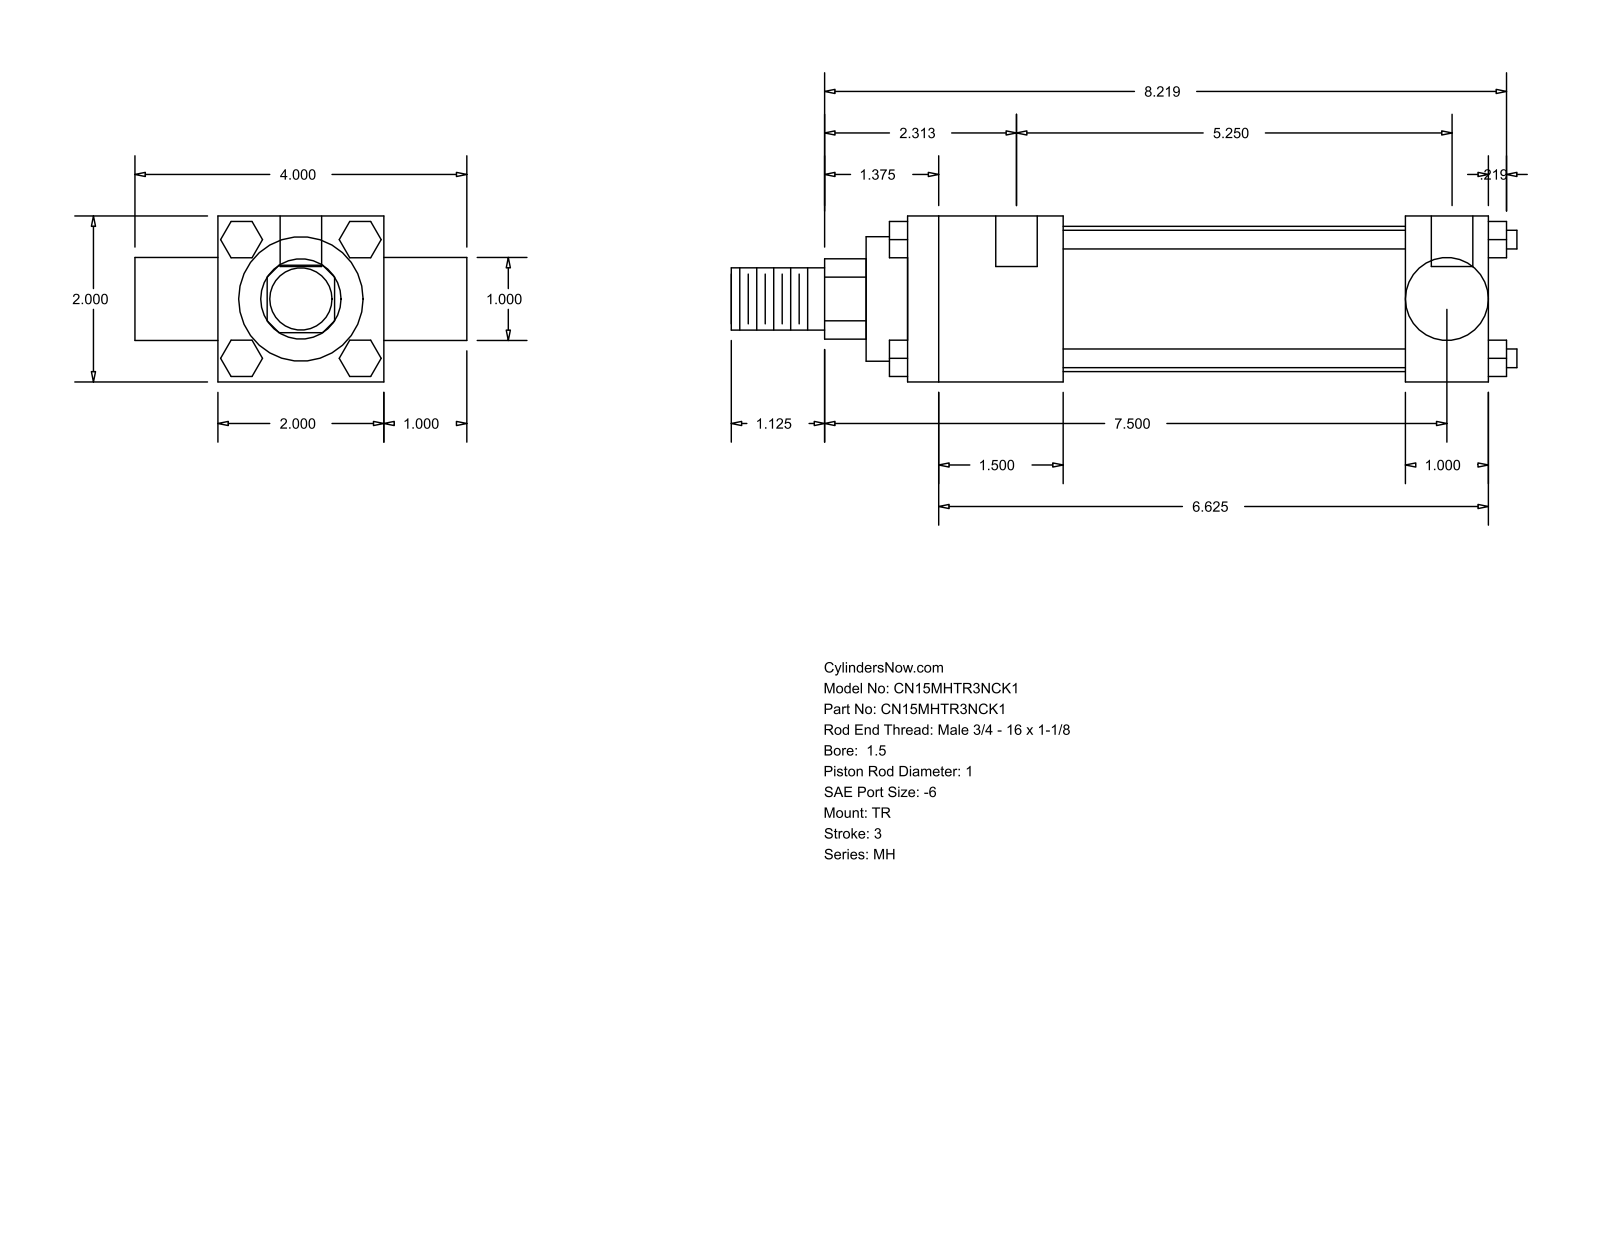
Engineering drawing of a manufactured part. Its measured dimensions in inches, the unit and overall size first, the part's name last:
Units: inches
Overall size (bounding box): 9.469 × 4 × 2
Round holes (diameter × count): ⌀0.219 ×3, ⌀0.5 ×2
Round bosses / shafts (diameter × count): ⌀0.225 ×4, ⌀1.75 ×1, ⌀1.5 ×1, ⌀1 ×1, ⌀0.998 ×1, ⌀0.75 ×1
Partial cylindrical surfaces — rounded edges, fillets, slot ends (radius × count): R0.484 ×1
Main face-to-face distances: 2, 1, 7, 3, 1.875, 5.125, 6, 4.125, 4, 0.5
Hole centre spacings: 0.125, 5.25, 5.375
Bodies: 0 solids, 120 faces (92 planar, 28 cylindrical, 0 other)
Part name (STEP PRODUCT): MH_TR__0150_1
STEP written by: GSSL Pune (CONFIG_CONTROL_DESIGN)
